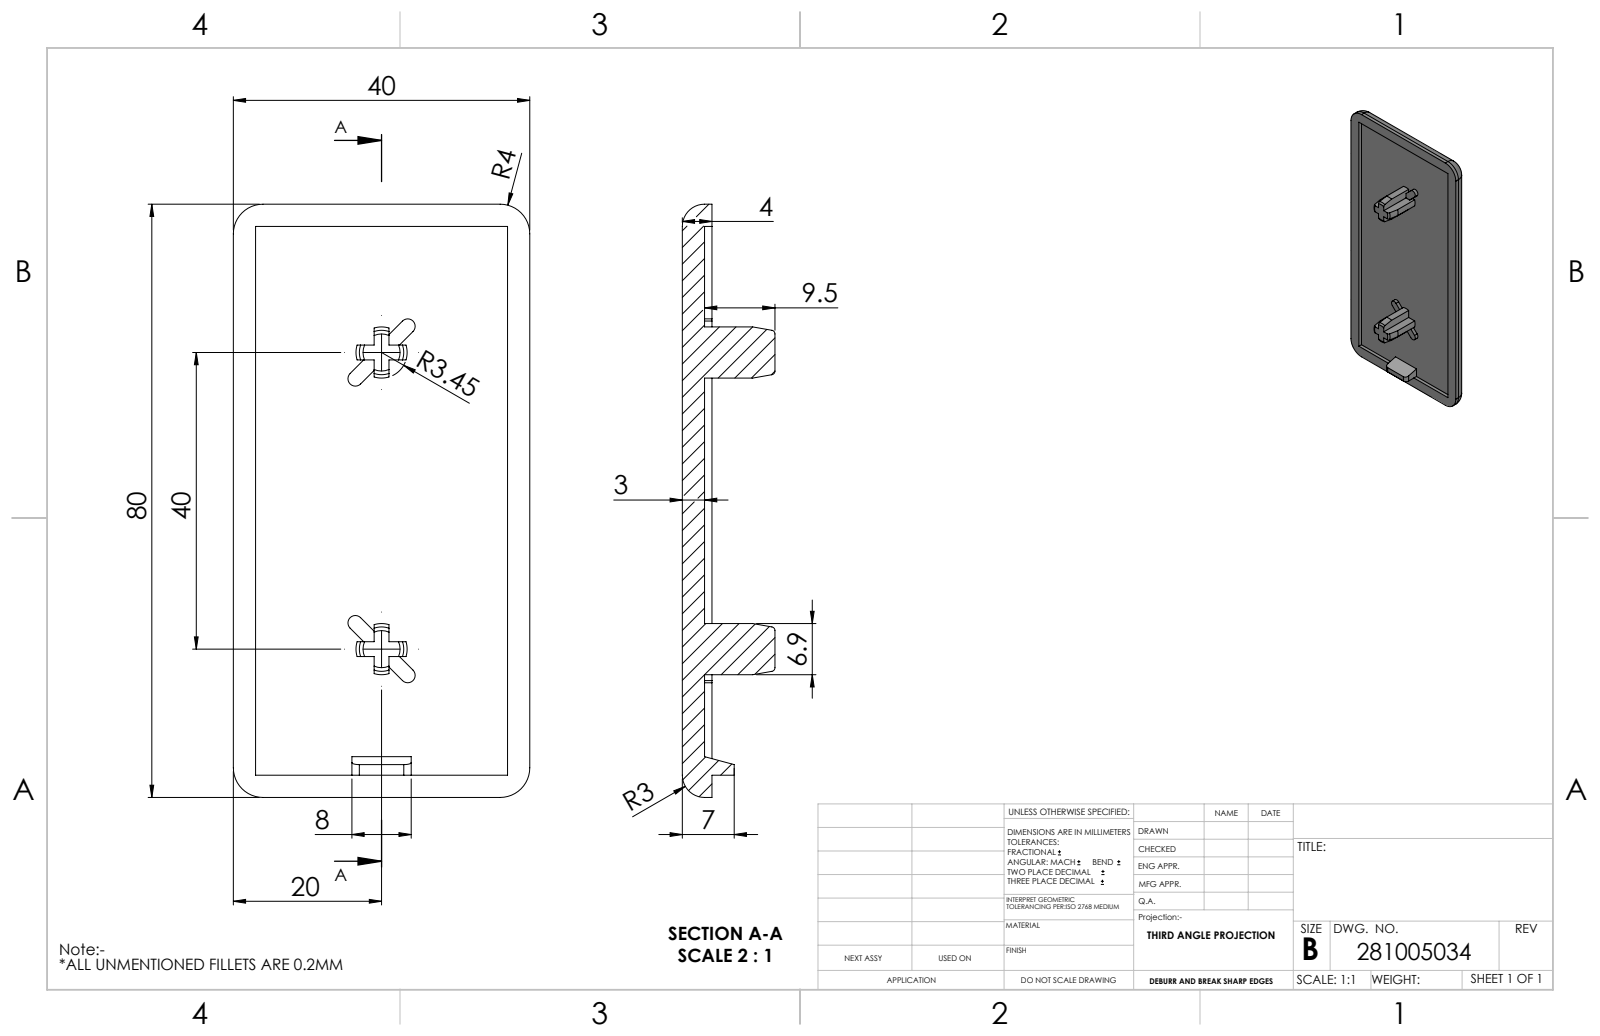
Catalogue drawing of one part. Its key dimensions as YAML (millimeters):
part_name: "281005034 Abdeckkappe 40x80 ESD"
step_written_by: "Autodesk Inventor 2019 (AUTOMOTIVE_DESIGN)"
units: millimeters
bodies: {solids: 1, faces: 89, planar: 47, cylindrical: 22, other: 20}
overall_size: [80, 40, 12.5]
volume: 10308
surface_area: 7773
partial_cylinders:
  - {radius: 1, count: 6}
  - {radius: 3, count: 4}
  - {radius: 4, count: 4}
  - {radius: 3.45, count: 2}
face_to_face_distances: [3, 4, 1, 16, 18, 21, 19, 2, 40, 37]
